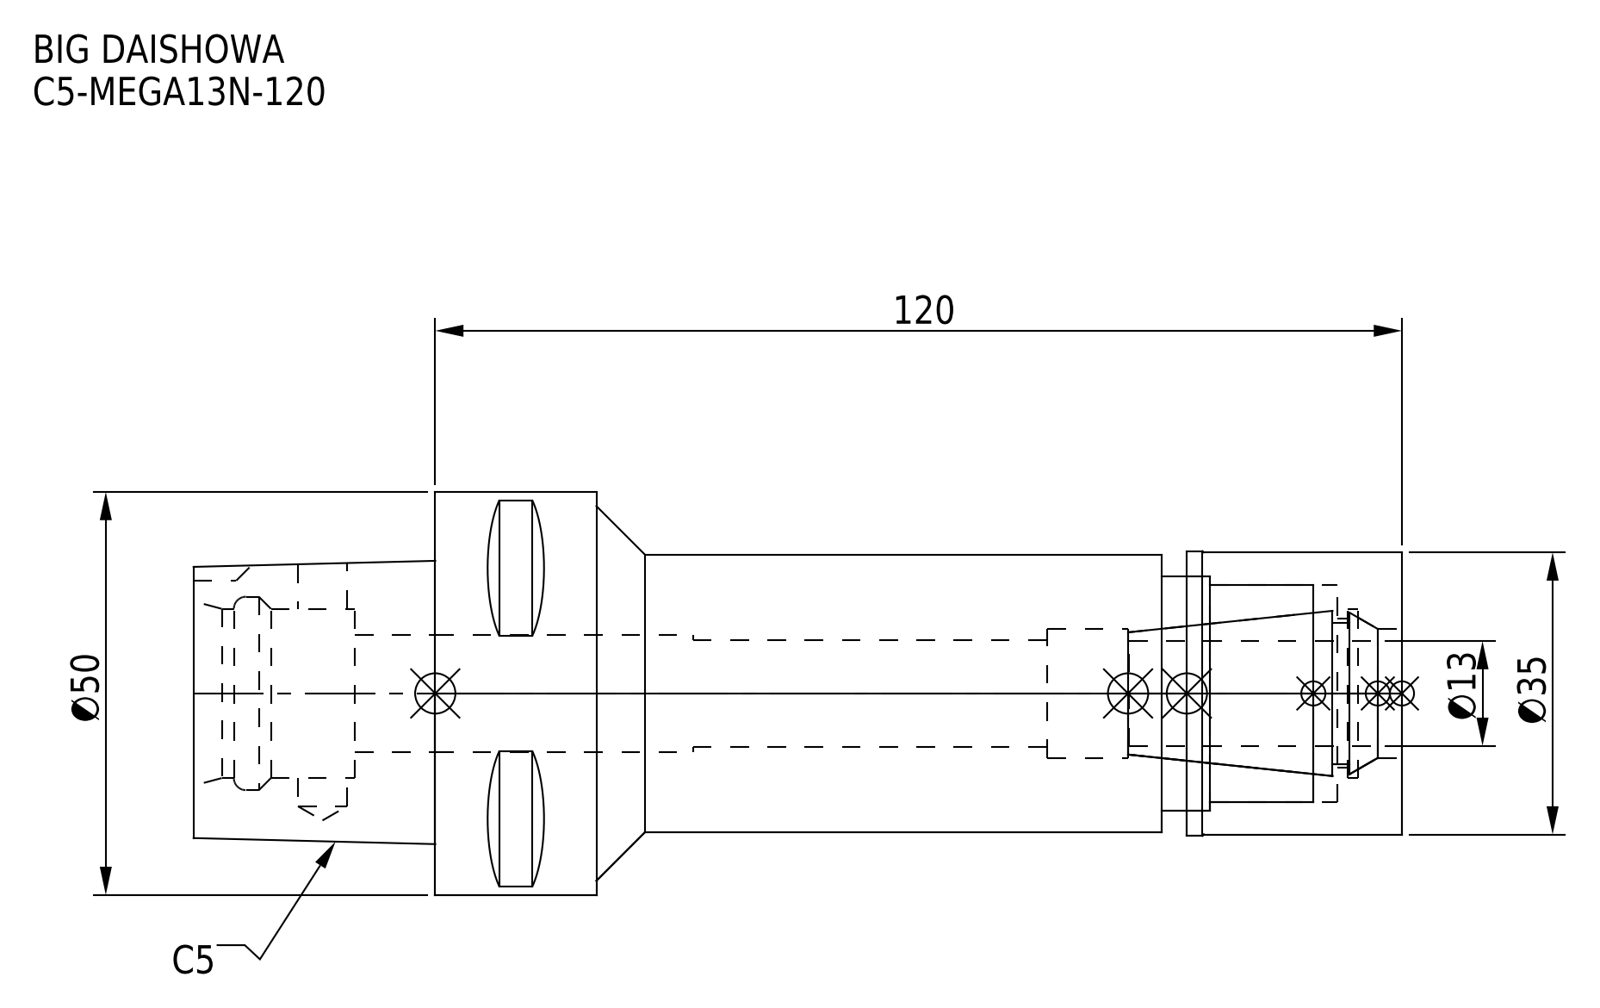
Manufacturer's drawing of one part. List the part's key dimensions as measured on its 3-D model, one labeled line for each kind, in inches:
Part name (STEP PRODUCT): C5-MEGA13N-120; C5-MEGA13N-120-130-FreeParts; C5-MEGA13N-120_1.stp; C5-MEGA13N-120-130_ASM.stp (+3 more)
STEP written by: SolidWorks 2019 (CONFIG_CONTROL_DESIGN)
Units: inches
Bodies: 2 solids, 95 faces (38 planar, 39 cylindrical, 18 other)
Overall size (bounding box): 5.906 × 1.969 × 1.969
Volume: 7.892 in³ · Surface area: 50.63 in²
Round holes (diameter × count): ⌀0.24 ×1, ⌀0.524 ×1, ⌀0.571 ×1, ⌀0.63 ×1, ⌀0.728 ×1, ⌀0.827 ×1, ⌀0.945 ×1, ⌀1.063 ×1, ⌀1.142 ×1
Round bosses / shafts (diameter × count): ⌀1.969 ×1, ⌀1.39 ×1, ⌀1.378 ×1, ⌀1.358 ×1
Partial cylindrical surfaces — rounded edges, fillets, slot ends (radius × count): R0.157 ×1
Main face-to-face distances: 4.724, 1.181, 0.787, 3.673, 4.854, 5.906, 1.051, 0.315, 0.736, 4.409
